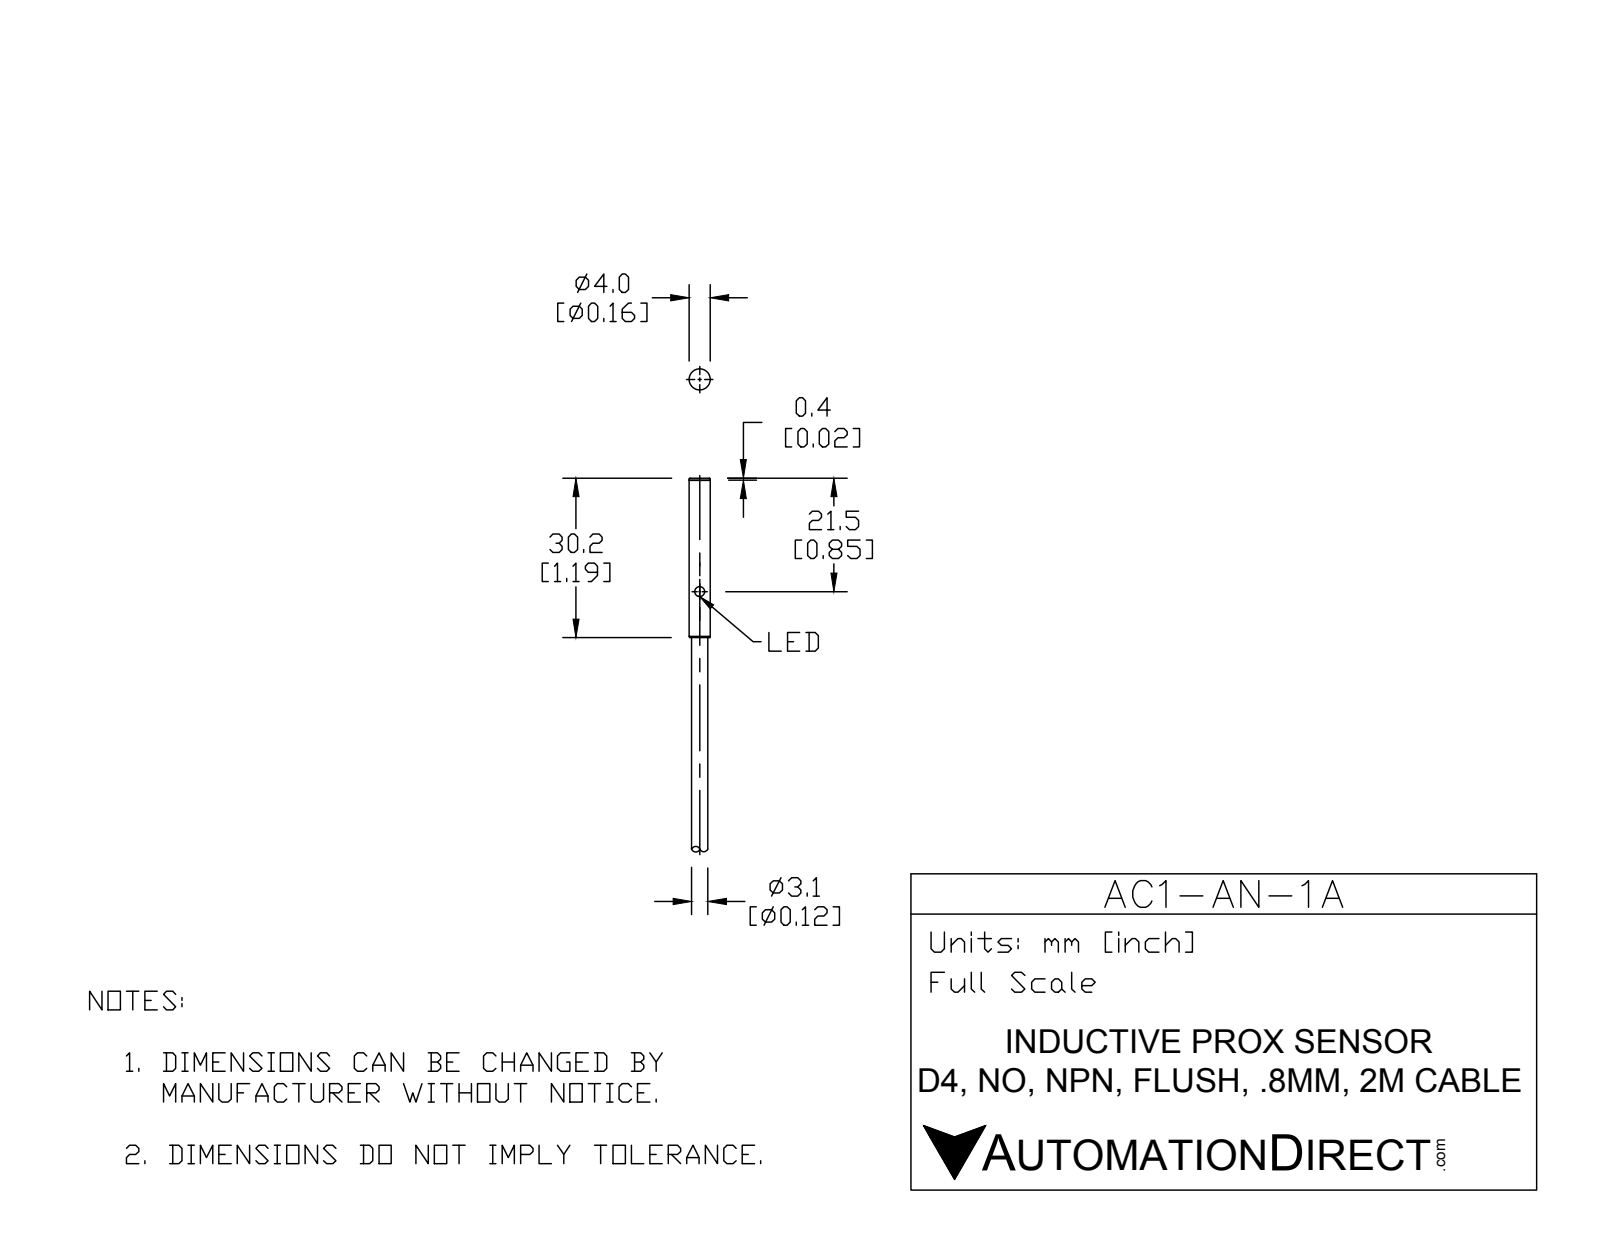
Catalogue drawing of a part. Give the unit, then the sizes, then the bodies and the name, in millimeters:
Units: millimetres
Overall size (bounding box): 80.2 × 4 × 4
Round holes (diameter × count): ⌀1.9 ×1
Round bosses / shafts (diameter × count): ⌀4 ×1, ⌀3.1 ×1
Main face-to-face distances: 30.2, 50, 80.2, 79.8, 29.8, 0.4
Volume: 756 mm³ · Surface area: 905 mm²
Bodies: 2 solids, 20 faces (6 planar, 8 cylindrical, 6 other)
Part name (STEP PRODUCT): AC1-AN-1A
STEP written by: SolidWorks 2015 (CONFIG_CONTROL_DESIGN)
